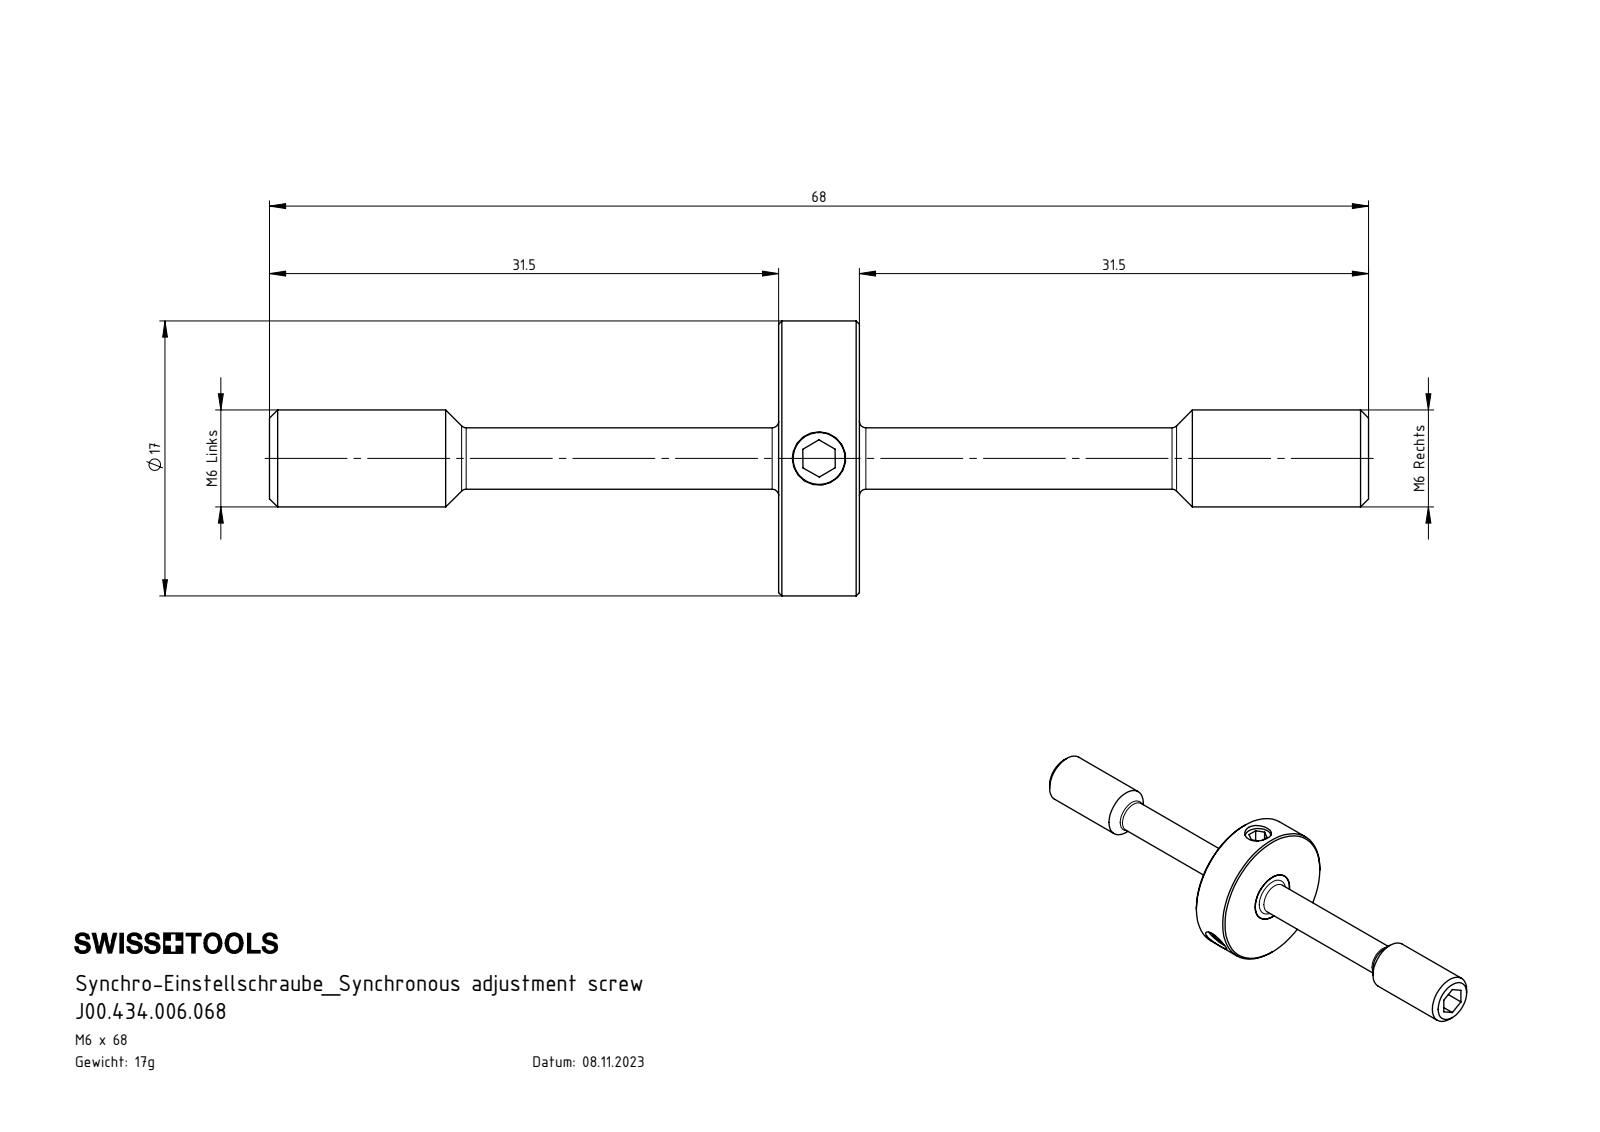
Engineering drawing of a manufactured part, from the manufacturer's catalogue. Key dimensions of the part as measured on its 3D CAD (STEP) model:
Part name (STEP PRODUCT): Z72-ER3.001.068_A; Z42-ER3.002.005_A; ISO 4026 - M4 x 5; J00.434.006.068
STEP written by: SolidWorks 2022 (AUTOMOTIVE_DESIGN)
Units: millimetres
Bodies: 5 solids, 99 faces (39 planar, 26 cylindrical, 34 other)
Overall size (bounding box): 68 × 17 × 17
Volume: 2 213 mm³ · Surface area: 2 285 mm²
Round holes (diameter × count): ⌀3.3 ×3
Round bosses / shafts (diameter × count): ⌀4 ×3, ⌀17 ×1, ⌀6 ×1, ⌀3.8 ×1
Main face-to-face distances: 5, 31.5, 36.5, 2, 2.5, 3, 68, 33, 35, 1.5
